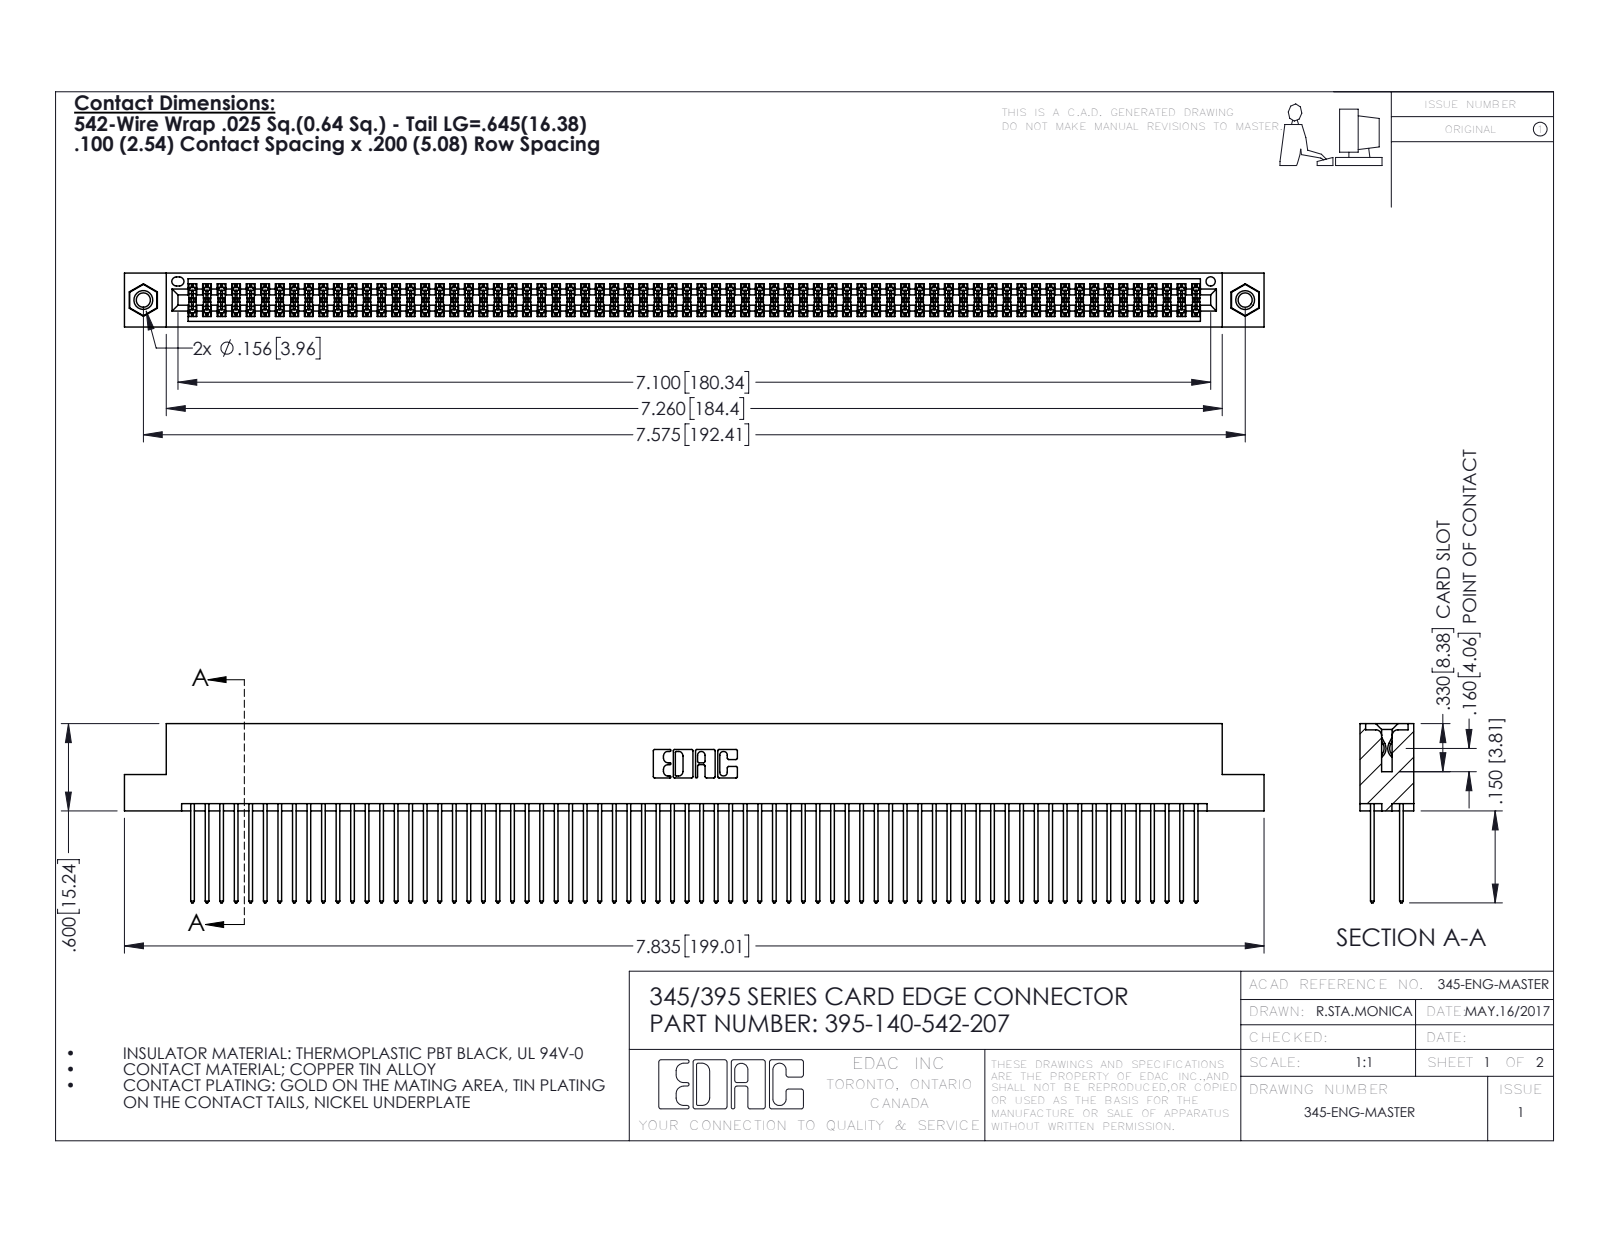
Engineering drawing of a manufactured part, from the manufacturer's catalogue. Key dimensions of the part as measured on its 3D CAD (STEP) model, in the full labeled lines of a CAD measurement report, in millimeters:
Part name (STEP PRODUCT): 345-250-001_345-250-005-103; 345 Part_Flush Mounting Lugs - 0.156 Dia-TI; 395-140-542-207; 345-292-001_345-293-142
STEP written by: SolidWorks 2016 (CONFIG_CONTROL_DESIGN)
Units: millimetres
Bodies: 143 solids, 7186 faces (4732 planar, 2438 cylindrical, 16 other)
Overall size (bounding box): 199 × 31.3 × 9.4
Volume: 20 240 mm³ · Surface area: 33 520 mm²
Round holes (diameter × count): ⌀2.5 ×2, ⌀3.2 ×2, ⌀4 ×2, ⌀1.6 ×1
Round bosses / shafts (diameter × count): ⌀3.9 ×2
Partial cylindrical surfaces — rounded edges, fillets, slot ends (radius × count): R0.2 ×210, R0.3 ×140, R0.3 ×22, R0.2 ×6, R0.8 ×6, R0.7 ×3, R0.4 ×2, R0.5 ×2
Main face-to-face distances: 1.8, 7.6, 5.1, 2.5, 6.9, 0.6, 5.7, 9.4, 4.4, 3.8
Hole centre spacings: 6.9, 186.4, 192.4
